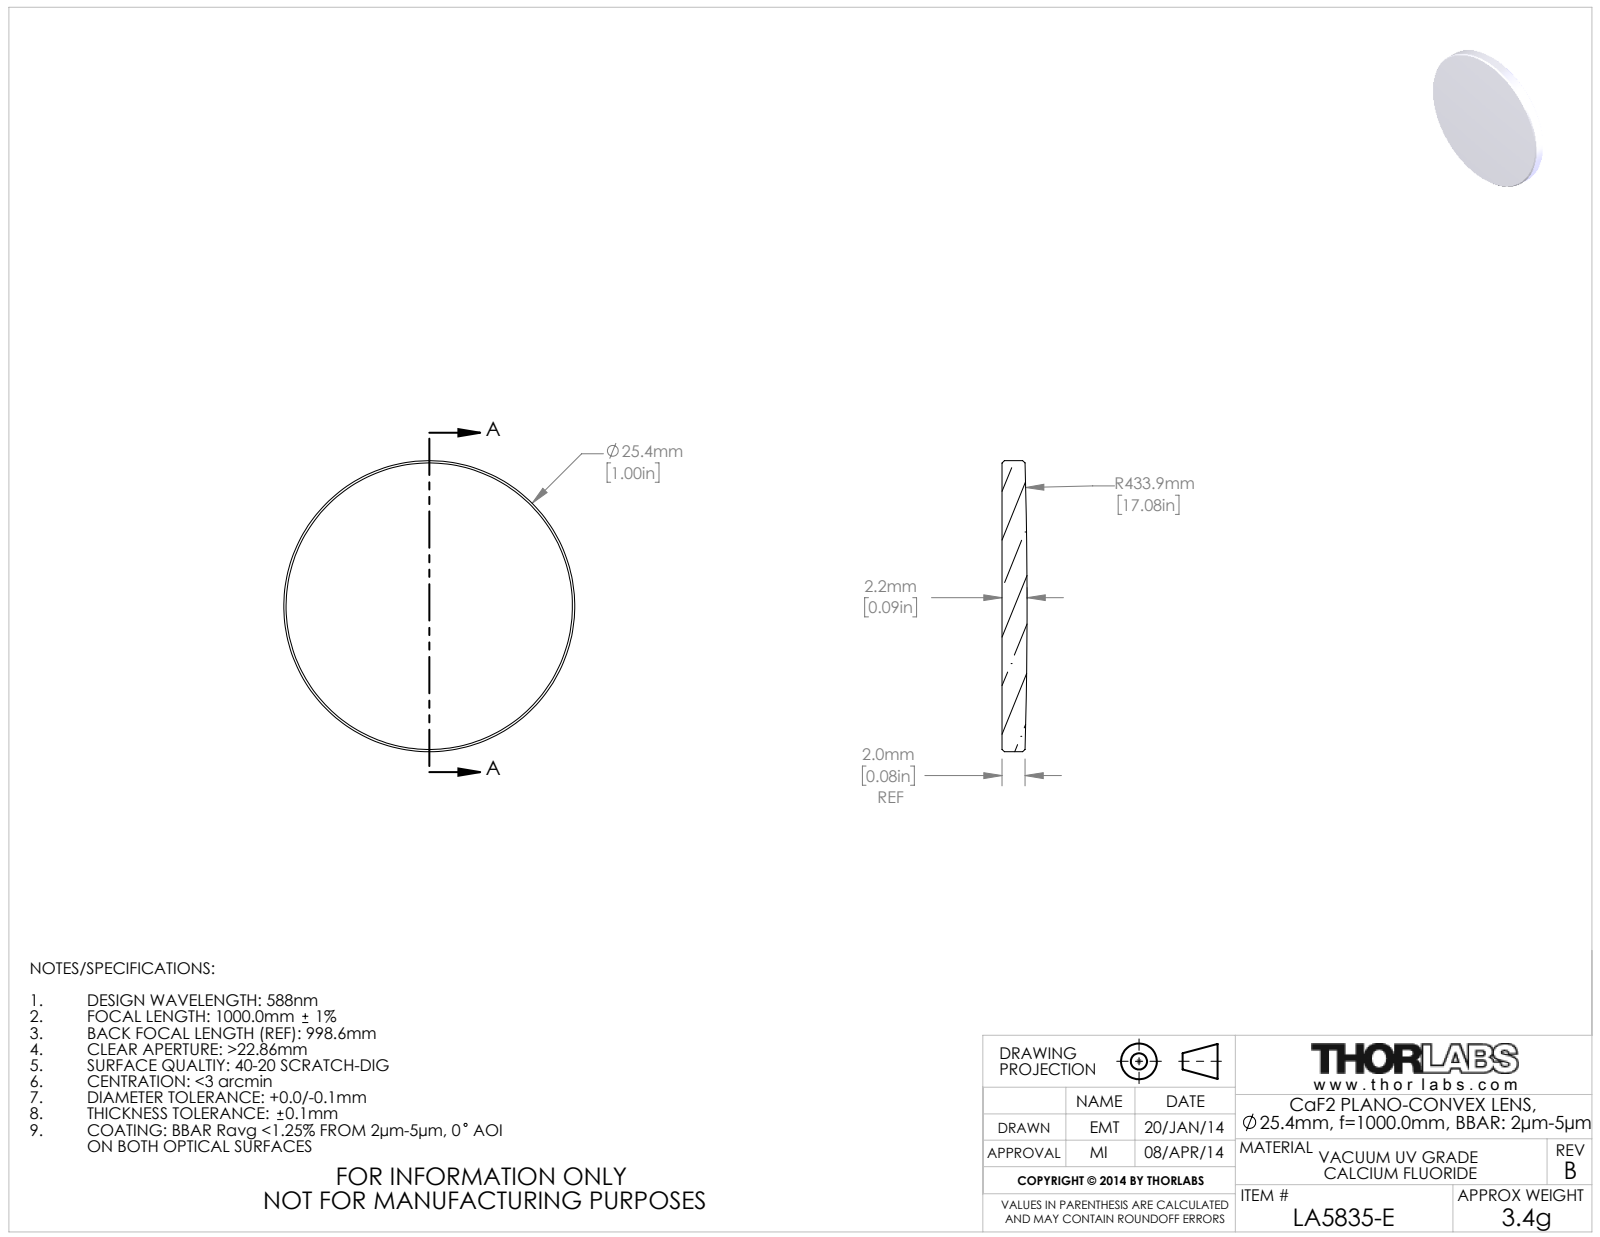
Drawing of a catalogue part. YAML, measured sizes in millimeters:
part_name: "20140-E0W"
step_written_by: "SolidWorks 2018 (CONFIG_CONTROL_DESIGN)"
units: millimeters
bodies: {solids: 1, faces: 9, planar: 1, cylindrical: 2, other: 6}
overall_size: [25.4, 25.4, 2.18]
volume: 1054
surface_area: 1154
round_bosses_or_shafts:
  - {diameter: 25.4, count: 1}
